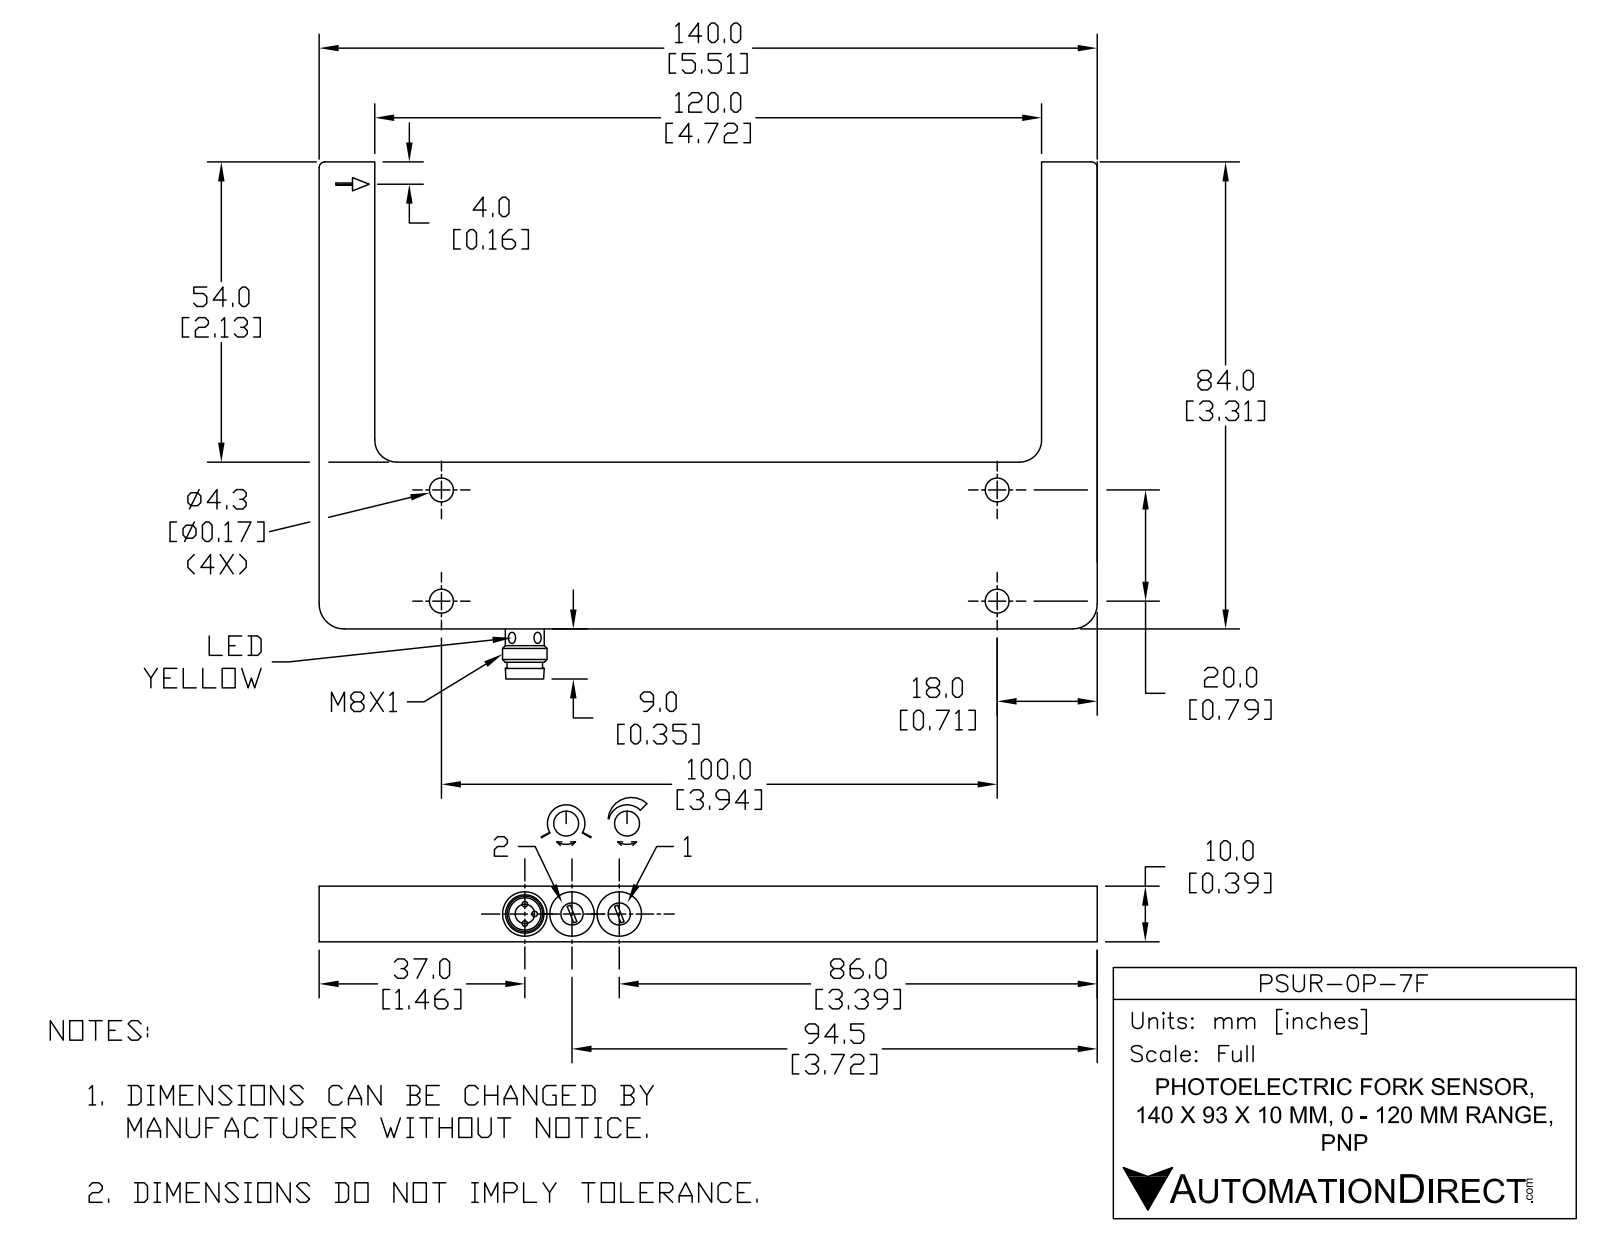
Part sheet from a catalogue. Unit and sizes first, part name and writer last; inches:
Units: inches
Overall size (bounding box): 5.512 × 3.661 × 0.394
Round holes (diameter × count): ⌀0.169 ×4, ⌀0.079 ×2, ⌀0.157 ×2, ⌀0.315 ×2, ⌀0.228 ×1
Round bosses / shafts (diameter × count): ⌀0.315 ×1, ⌀0.267 ×1
Partial cylindrical surfaces — rounded edges, fillets, slot ends (radius × count): R0.063 ×2, R0.157 ×2, R0.197 ×2
Main face-to-face distances: 0.394, 1.181, 5.118, 5.512, 4.724, 2.126, 3.307, 3.303, 1.177, 0.157
Hole centre spacings: 0.335, 0.787, 3.937, 4.015, 0.669
Volume: 3.197 in³ · Surface area: 26.03 in²
Bodies: 1 solid, 81 faces (35 planar, 40 cylindrical, 6 other)
Part name (STEP PRODUCT): PSUR-0P-7F
STEP written by: SolidWorks 2016 (AUTOMOTIVE_DESIGN)
